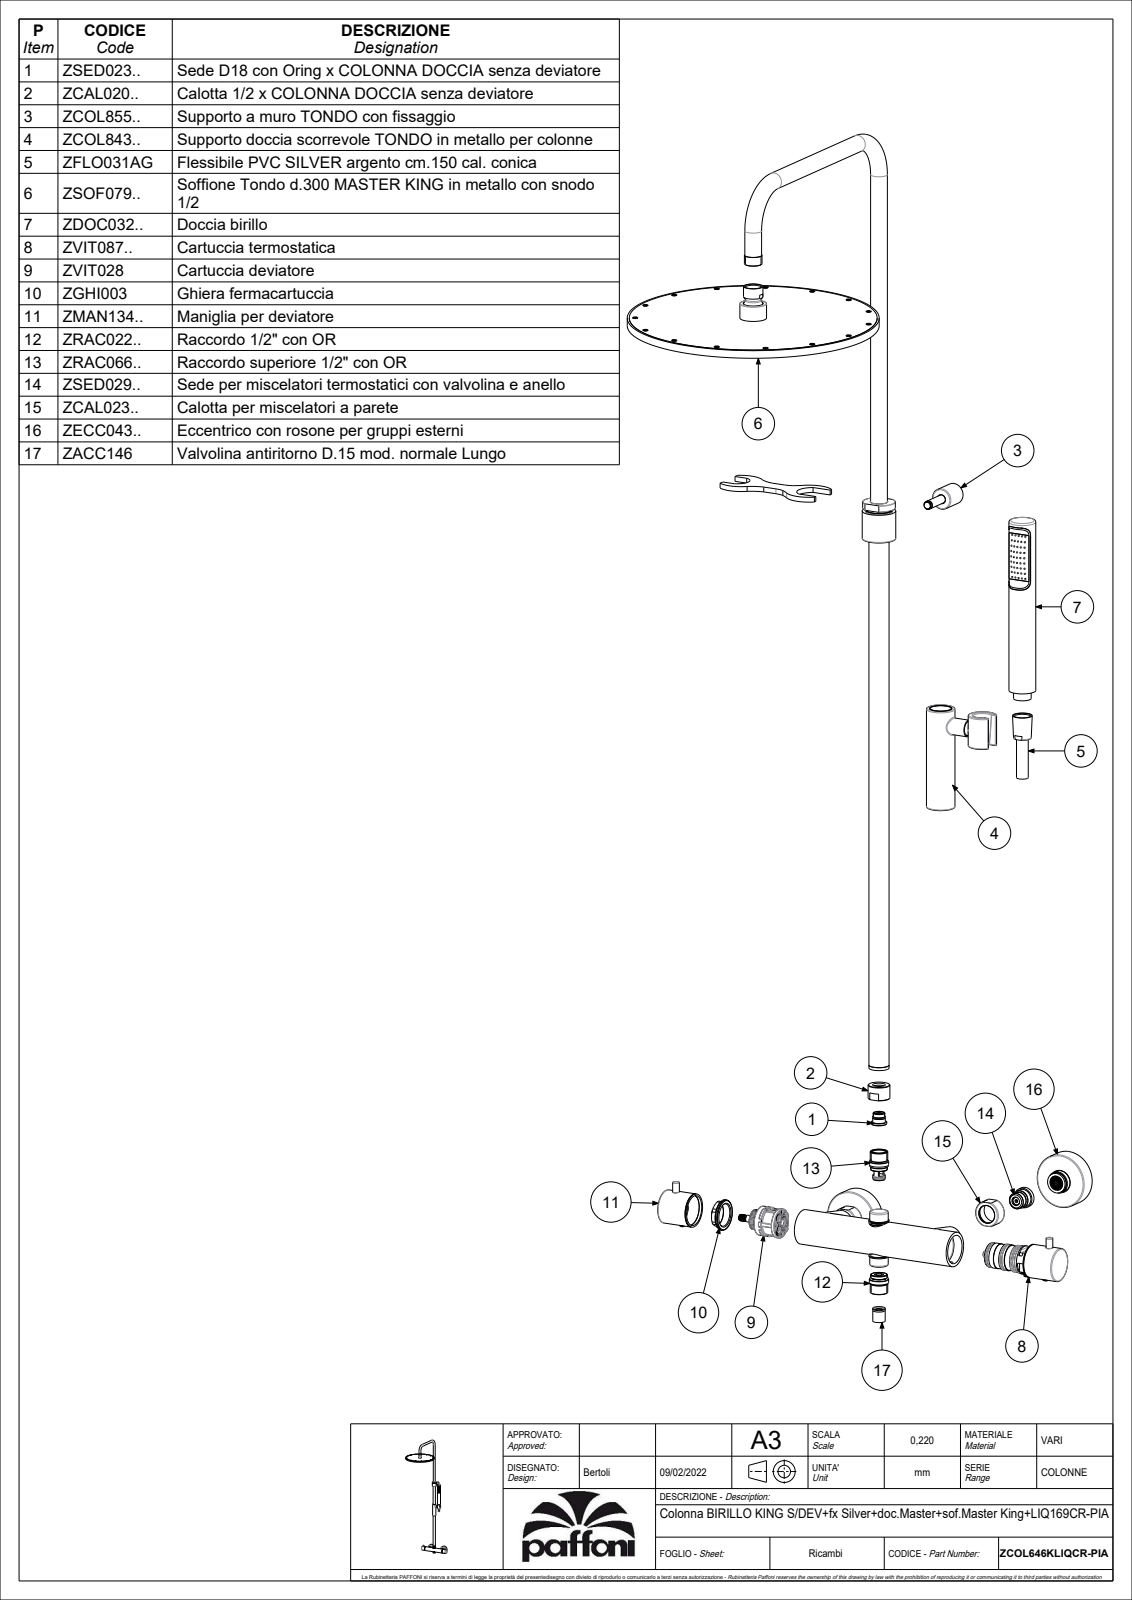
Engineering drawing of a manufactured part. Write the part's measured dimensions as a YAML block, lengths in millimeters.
part_name: "ZCOL646KLIQCR-PIA"
step_written_by: "CREO PARAMETRIC BY PTC INC, 2022124 (CONFIG_CONTROL_DESIGN)"
units: millimeters
bodies: {solids: 12, faces: 12086, planar: 1436, cylindrical: 2571, other: 8079}
overall_size: [1236.1, 532.92, 300.44]
volume: 776600
surface_area: 801929
round_holes:
  - {diameter: 1.5, count: 261}
  - {diameter: 1.7, count: 216}
  - {diameter: 2.5, count: 17}
  - {diameter: 5.1, count: 15}
  - {diameter: 4, count: 4}
  - {diameter: 7, count: 4}
  - {diameter: 15.1, count: 4}
  - {diameter: 17, count: 4}
  - {diameter: 25, count: 3}
  - {diameter: 3.25, count: 2}
  - {diameter: 3.3, count: 2}
  - {diameter: 5, count: 2}
round_bosses_or_shafts:
  - {diameter: 5, count: 231}
  - {diameter: 10, count: 217}
  - {diameter: 6, count: 15}
  - {diameter: 20, count: 4}
  - {diameter: 40, count: 3}
  - {diameter: 24, count: 3}
  - {diameter: 8, count: 3}
  - {diameter: 64.5, count: 2}
partial_cylinders:
  - {radius: 1.5, count: 64}
  - {radius: 0.3, count: 24}
  - {radius: 20, count: 15}
  - {radius: 1, count: 13}
  - {radius: 1.75, count: 4}
  - {radius: 4, count: 2}
  - {radius: 6.5, count: 2}
  - {radius: 7.8, count: 2}
face_to_face_distances: [1, 8.5, 9.5, 8, 1.5, 7, 2.2, 0.7, 6.3, 7.3]
hole_center_spacings: [69, 7.91, 13.76, 6.5, 20.01, 13, 26.39, 47.2]
